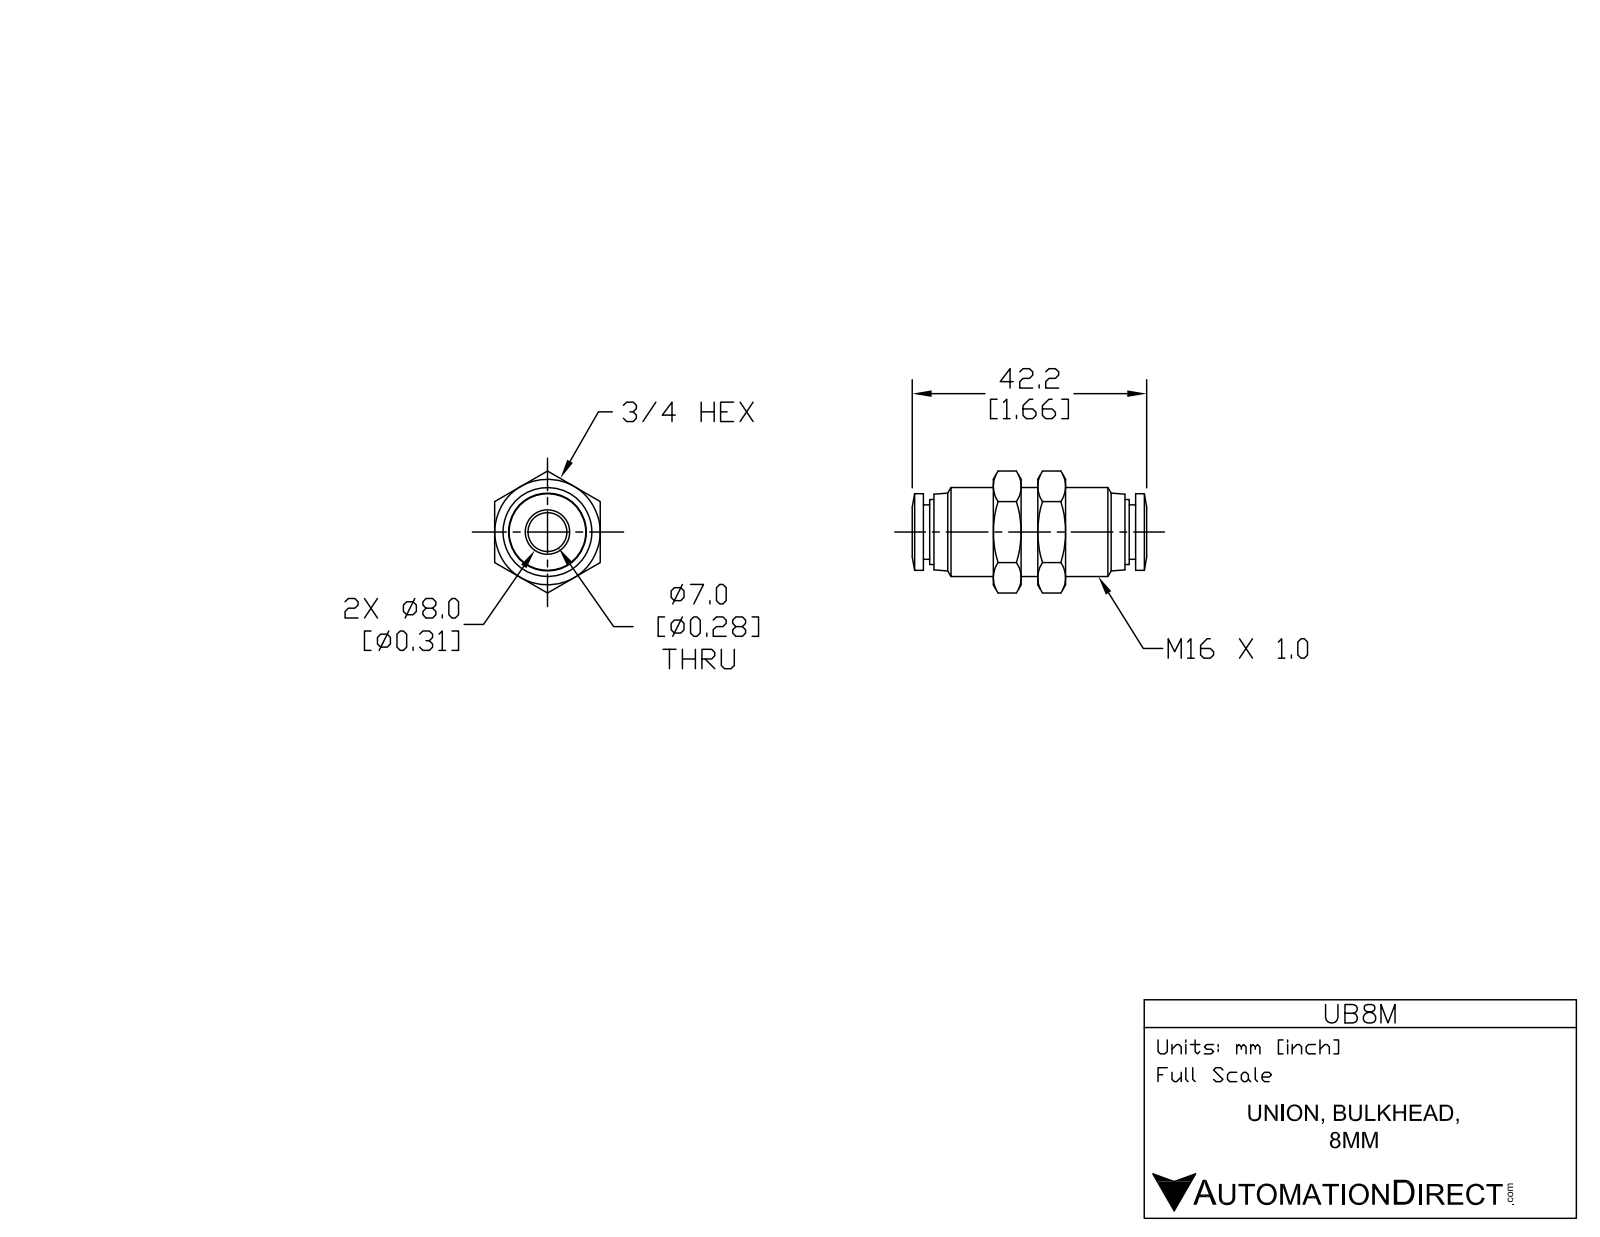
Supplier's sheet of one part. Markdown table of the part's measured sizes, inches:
| quantity | value |
| --- | --- |
| part name | UB8M |
| STEP written by | SolidWorks 2015 (AUTOMOTIVE_DESIGN) |
| units | inches |
| bodies | 1 solid, 94 faces (26 planar, 24 cylindrical, 44 other) |
| overall size | 1.661 × 0.864 × 0.748 |
| volume | 0.392 in³ |
| surface area | 6.414 in² |
| round holes (diameter × count) | 0.276 × 1, 0.327 × 1 |
| round bosses / shafts (diameter × count) | 0.63 × 1, 0.543 × 1, 0.461 × 1, 0.386 × 1 |
| main face-to-face distances | 0.748, 0.197, 0.315, 0.496, 0.693, 0.811, 1.008, 0.512, 0.118, 0.075 |
